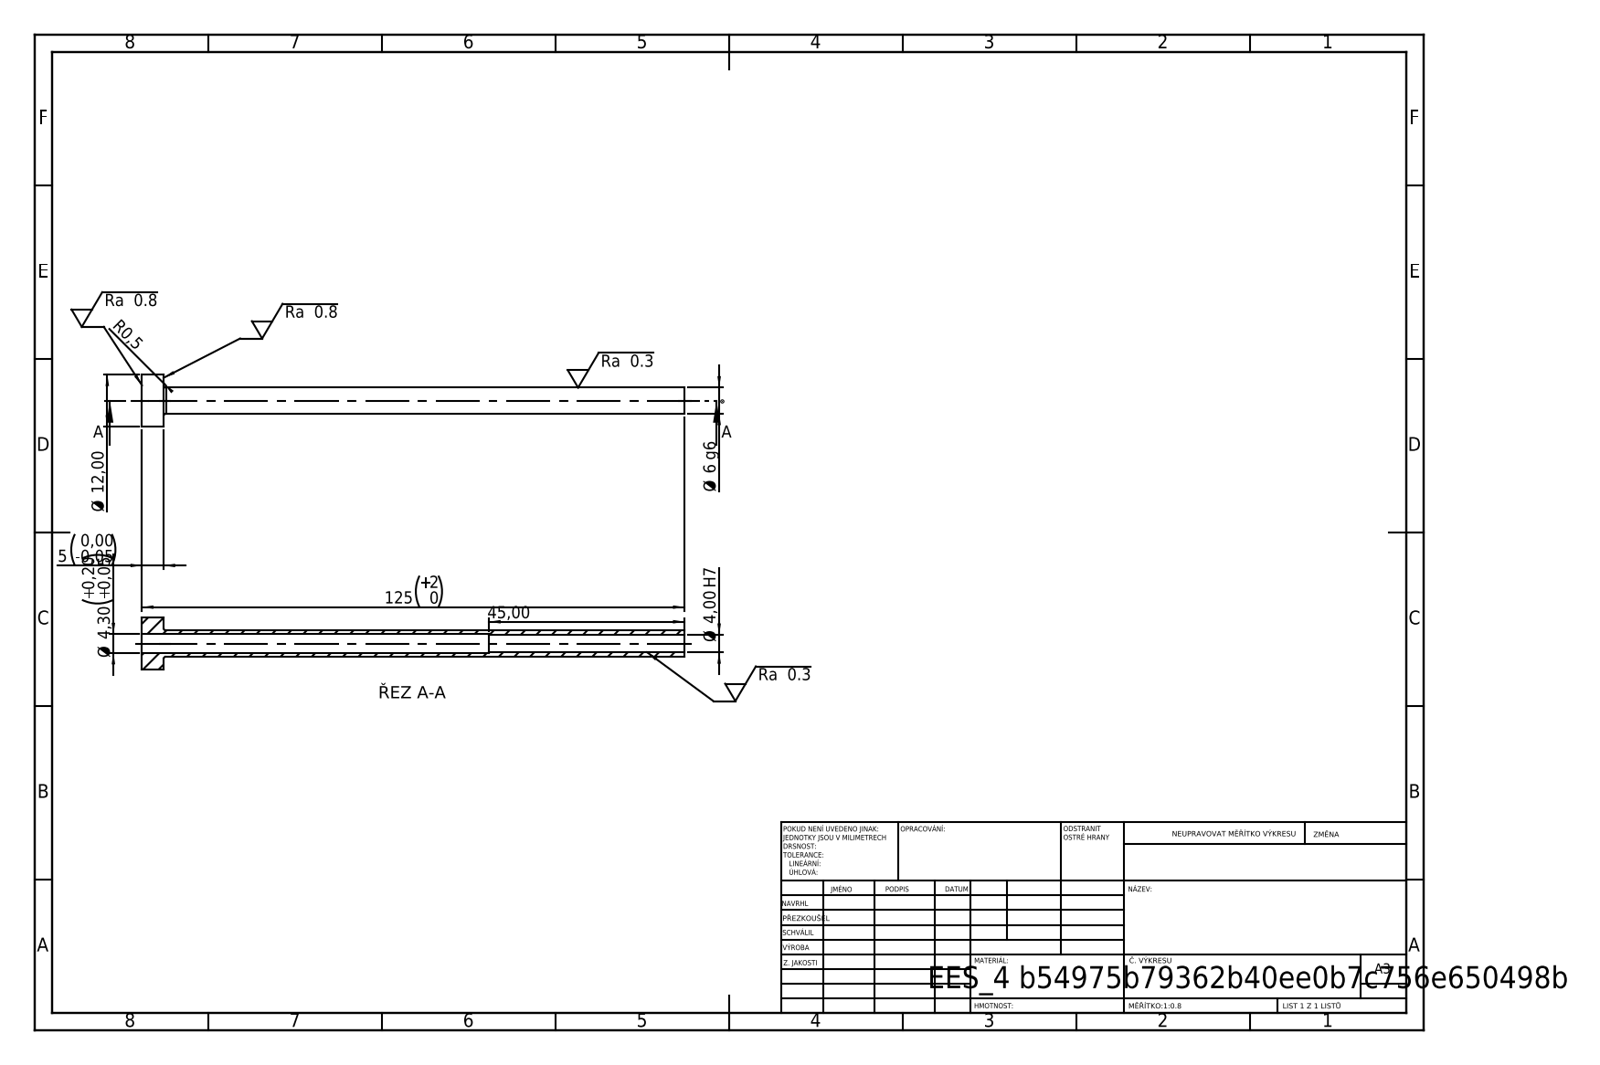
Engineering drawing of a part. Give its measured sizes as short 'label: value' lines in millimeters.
written by: SolidWorks 2019 (CONFIG_CONTROL_DESIGN)
unit: mm
bodies: 1 solid, 14 faces (4 planar, 8 cylindrical, 2 other)
size: 125 × 12 × 12
volume: 2 232 mm³; area: 4 294 mm²
holes: 1× ⌀4, 1× ⌀4.3
bosses: 1× ⌀12, 1× ⌀6
face distances: 5, 125, 120, 80, 75, 45
